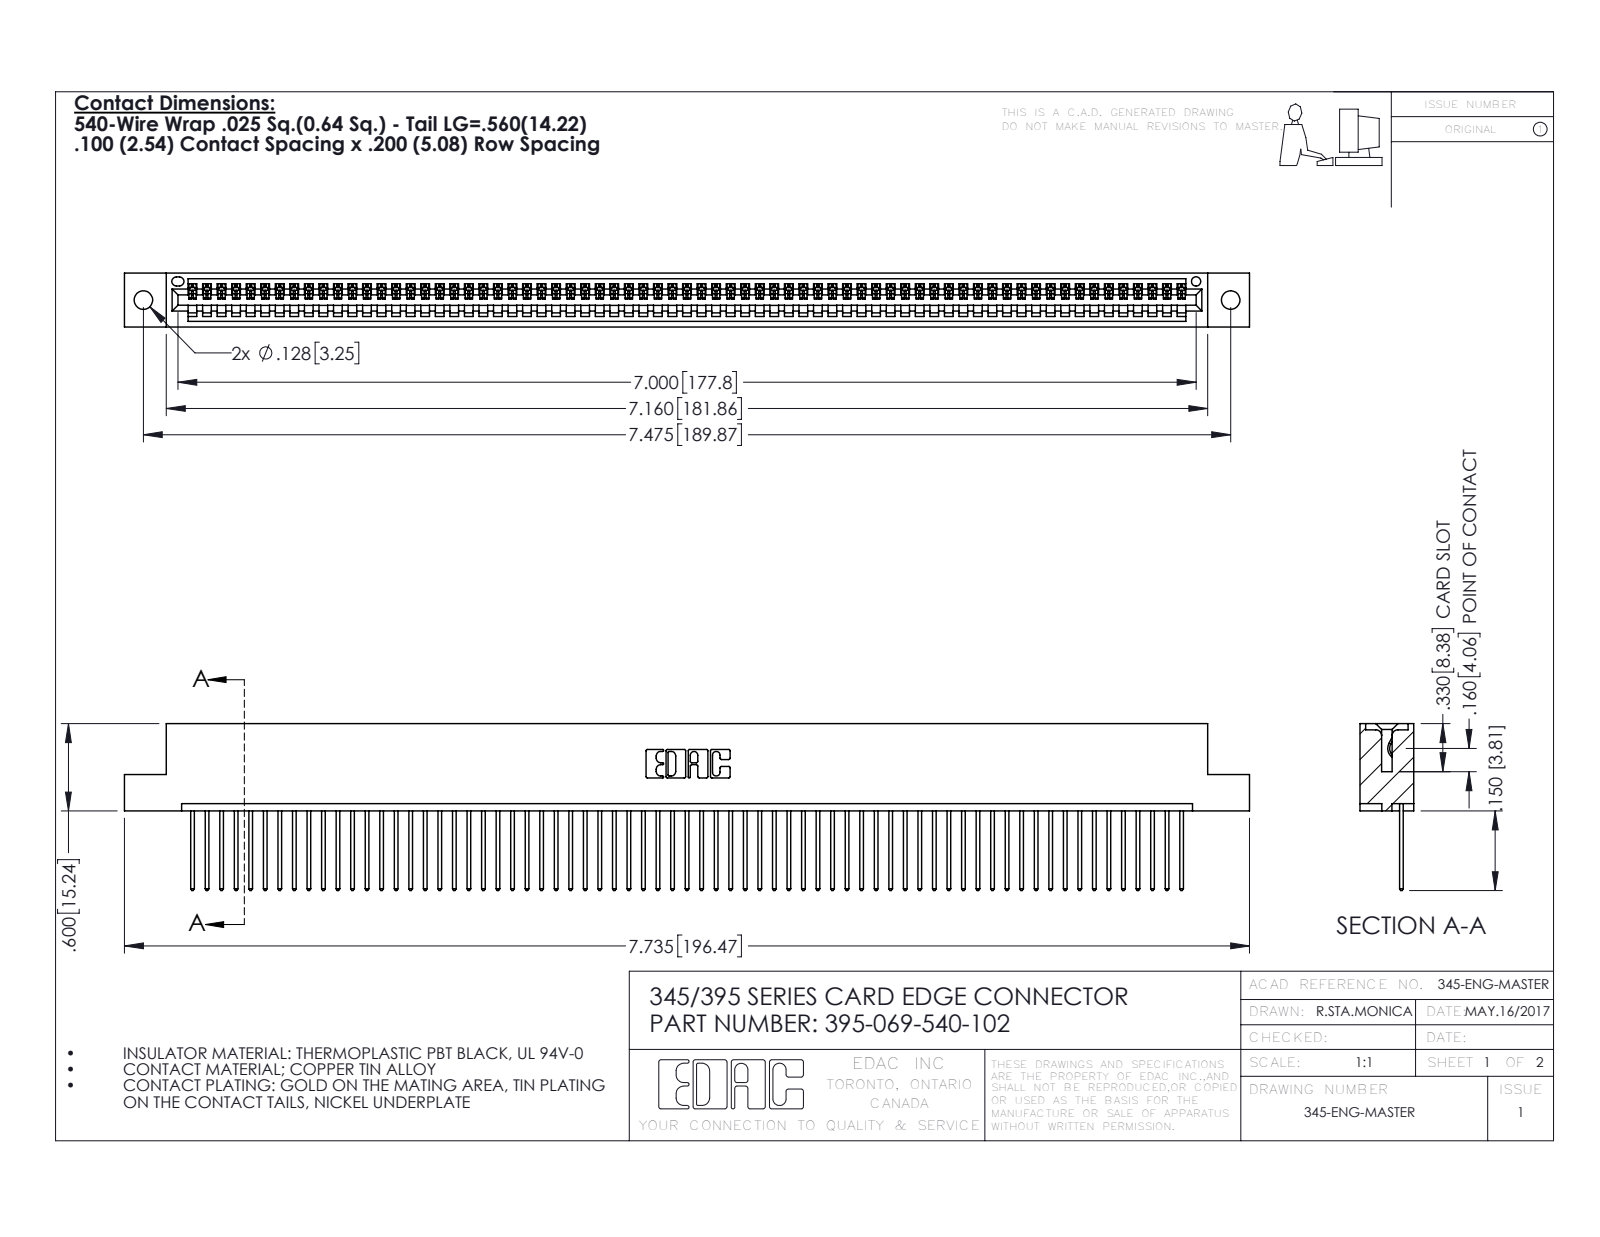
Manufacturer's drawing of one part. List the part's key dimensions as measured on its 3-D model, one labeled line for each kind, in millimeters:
Part name (STEP PRODUCT): 395-069-540-102; 345-292-001_345-293-140; 345 Part_Flush Mounting Lugs - 0.128 Dia
STEP written by: SolidWorks 2016 (CONFIG_CONTROL_DESIGN)
Units: millimetres
Bodies: 70 solids, 4128 faces (2840 planar, 1288 cylindrical, 0 other)
Overall size (bounding box): 196.5 × 29.1 × 9.4
Volume: 18 940 mm³ · Surface area: 25 940 mm²
Round holes (diameter × count): ⌀3.3 ×2, ⌀1.6 ×1
Partial cylindrical surfaces — rounded edges, fillets, slot ends (radius × count): R0.2 ×138, R0.3 ×138, R0.3 ×22, R0.2 ×6, R0.8 ×6, R0.7 ×3, R0.8 ×2, R1 ×2
Main face-to-face distances: 1.8, 7.6, 9.4, 2.5, 6.9, 0.6, 5.1, 5.7, 3.8, 1.8
Hole centre spacings: 6.9, 183.9, 189.9
